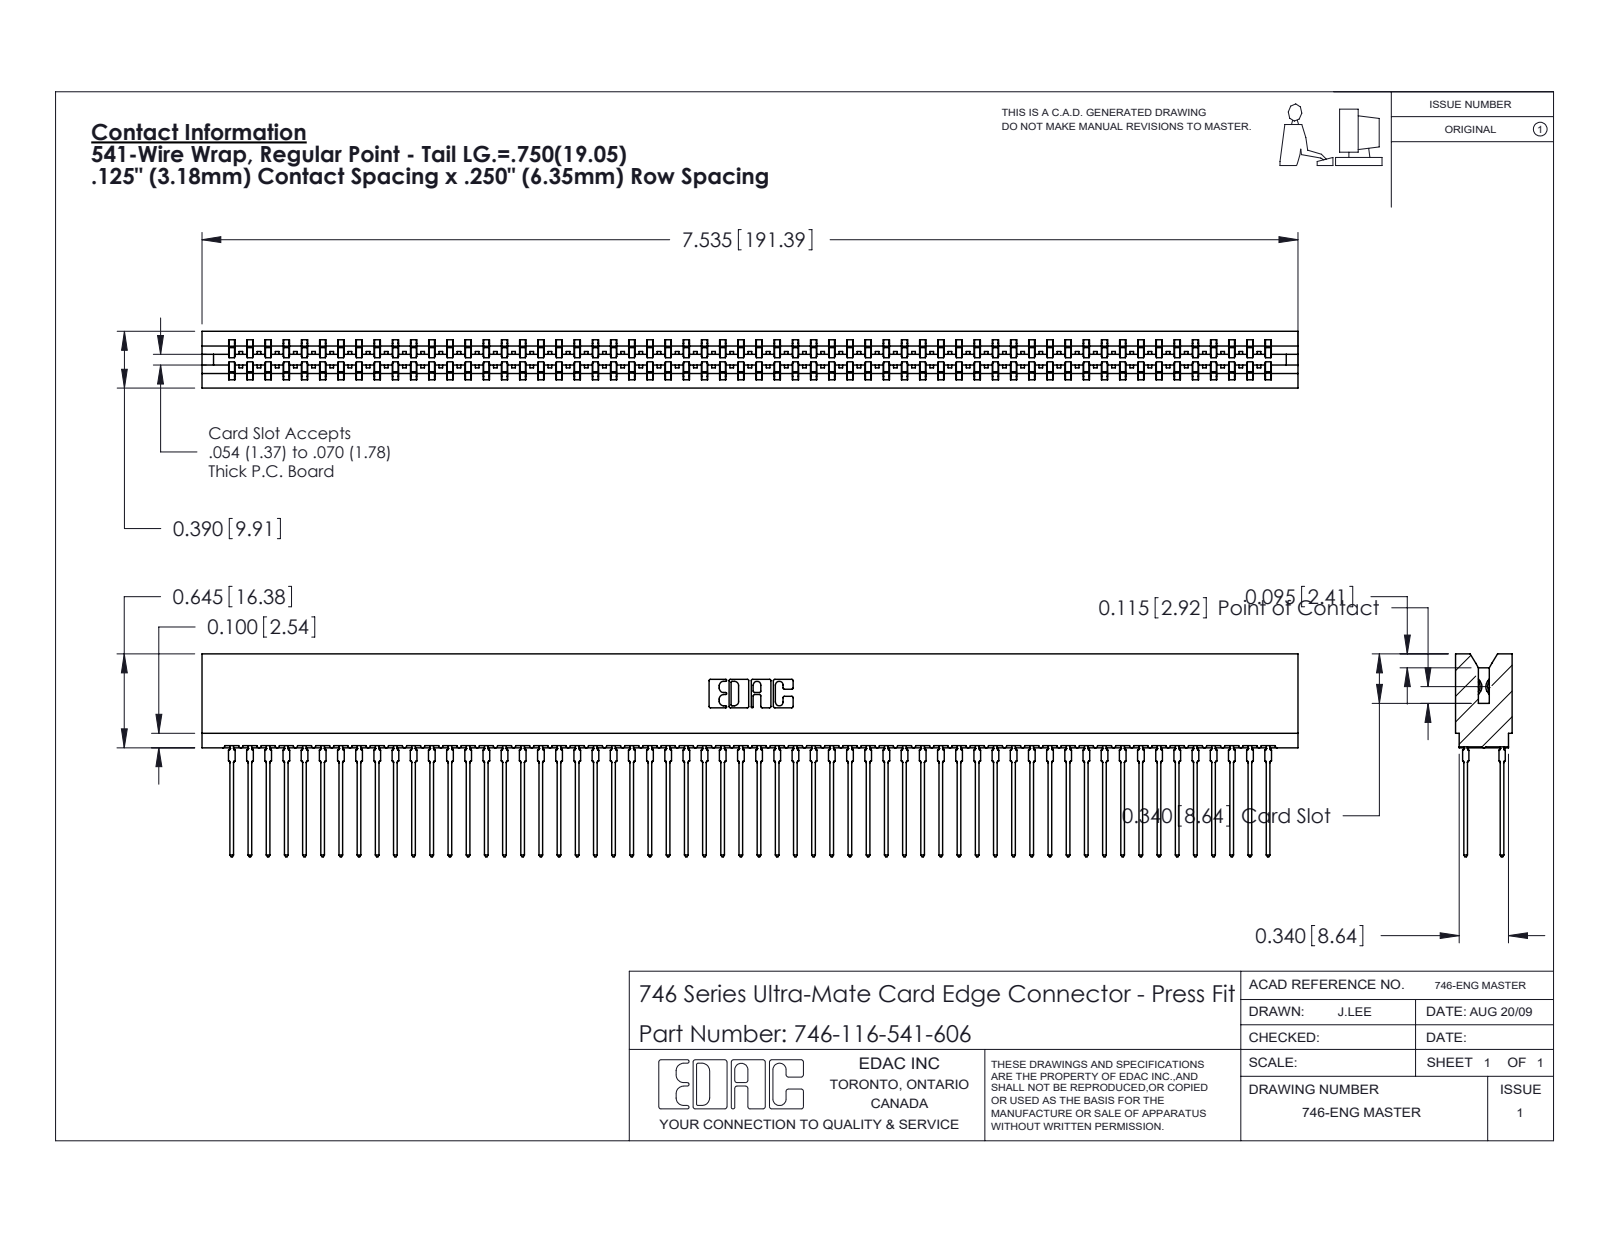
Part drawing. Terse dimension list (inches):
name: 746 Part_.340 Slot Depth - 06; 746-292-001_541; 746-116-541-606
written by: SolidWorks 2020 (CONFIG_CONTROL_DESIGN)
unit: in
bodies: 117 solids, 10480 faces (5392 planar, 2072 cylindrical, 3016 other)
size: 7.535 × 1.394 × 0.39
volume: 1.375 in³; area: 56.42 in²
rounds: 232× R0.021, 59× R0.015, 22× R0.01, 8× R0.005, 8× R0.011, 6× R0.007, 6× R0.031, 3× R0.026
face distances: 0.057, 0.333, 0.25, 0.025, 0.307, 0.39, 0.083, 0.275, 0.225, 0.015
